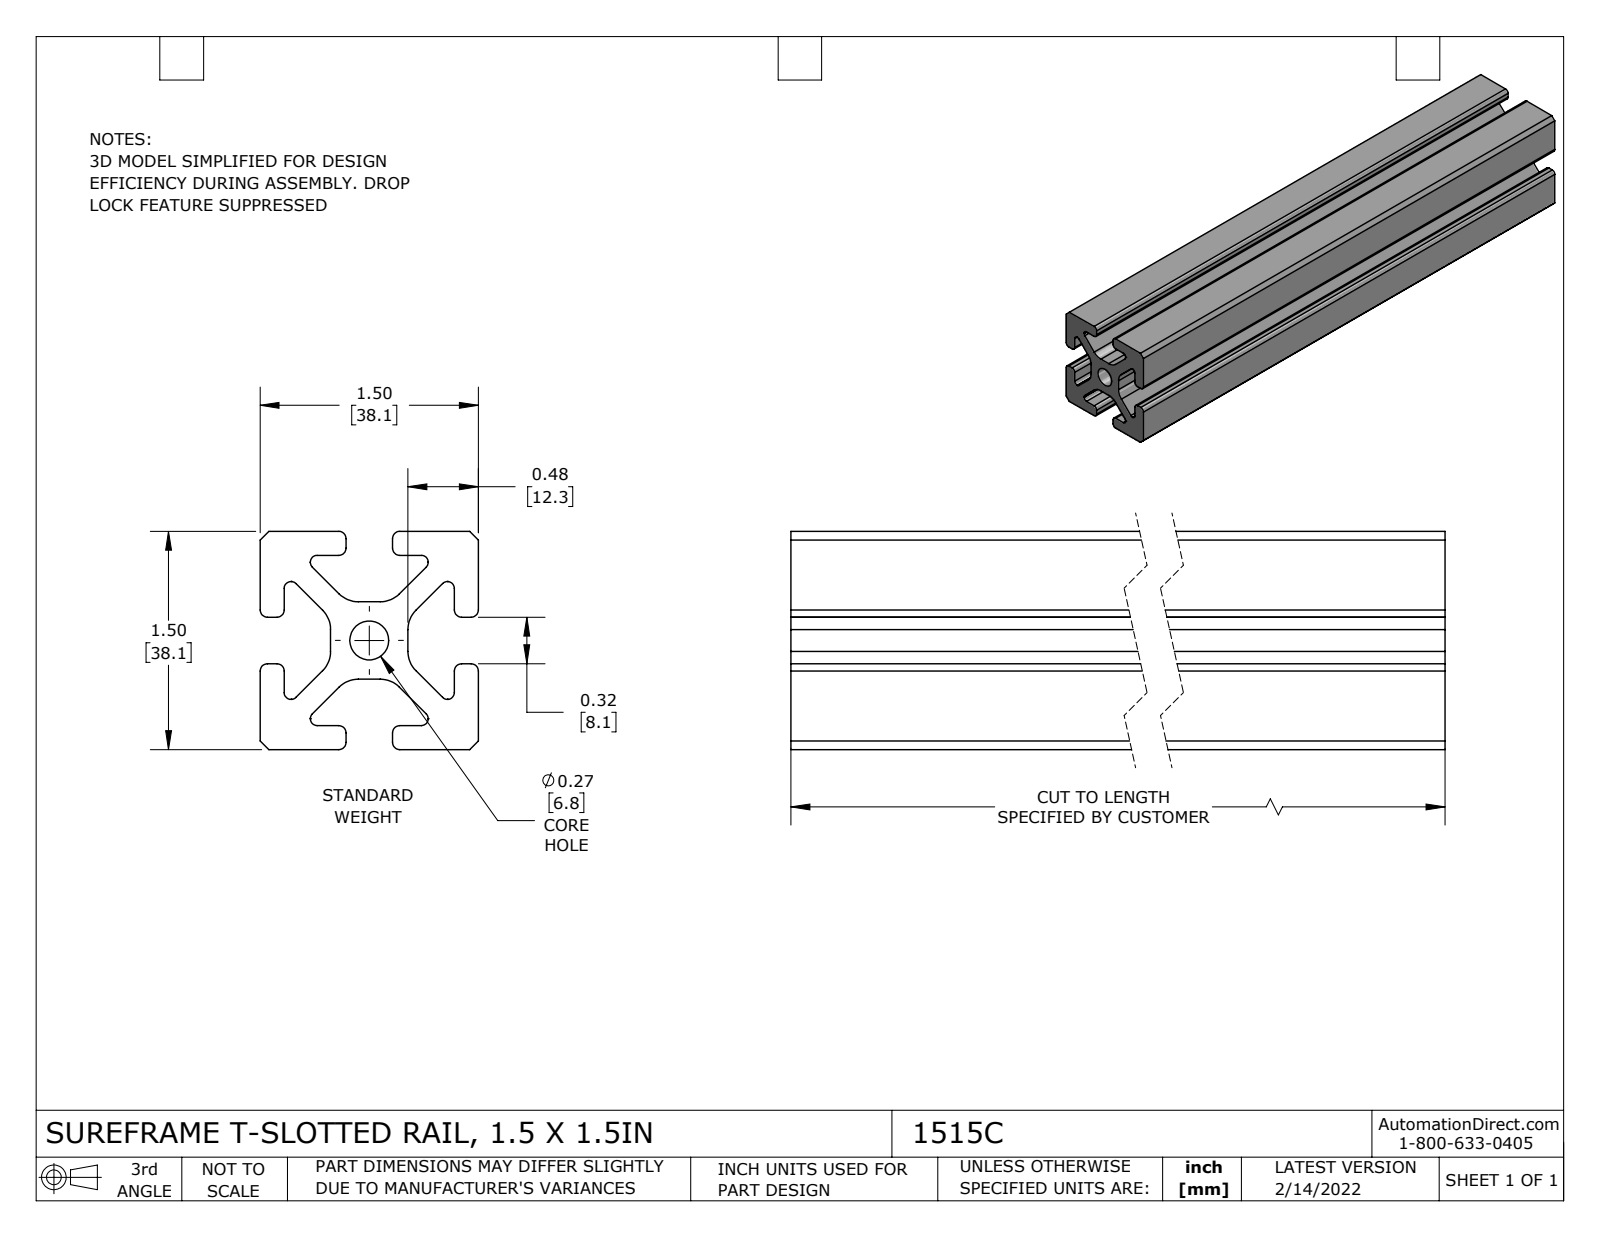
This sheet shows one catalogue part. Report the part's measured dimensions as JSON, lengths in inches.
{"part_name": "1515C", "step_written_by": "SolidWorks 2021 (CONFIG_CONTROL_DESIGN)", "units": "inches", "bodies": {"solids": 1, "faces": 92, "planar": 50, "cylindrical": 42, "other": 0}, "overall_size": [8, 1.5, 1.5], "volume_in3": 9.582, "surface_area_in2": 104.2, "round_holes": [[0.268, 1]], "partial_cylinders_radius": [[0.047, 16], [0.05, 16], [0.188, 7], [0.187, 1]], "face_to_face_distances": [1.5, 0.165, 1.335, 0.16, 0.484, 1.016, 0.319, 0.851, 1.17, 0.59]}
